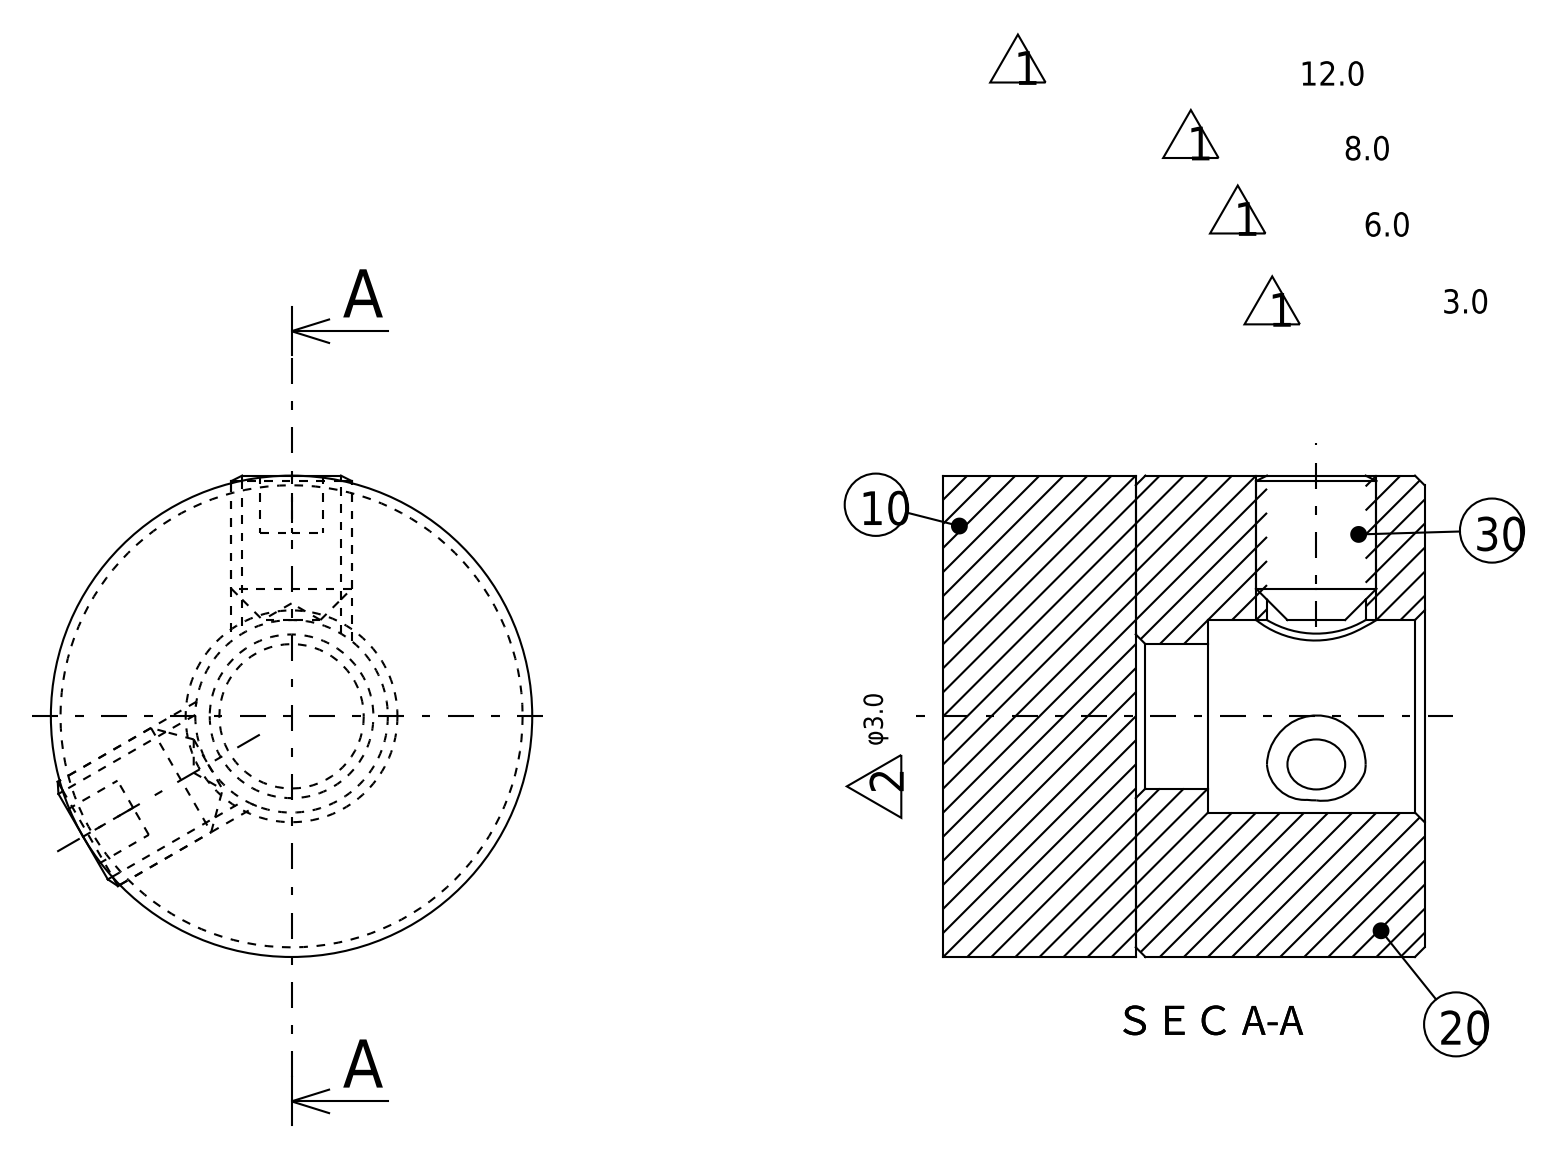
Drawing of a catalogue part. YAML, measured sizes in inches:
step_written_by: "PSStep 10.0 (CONFIG_CONTROL_DESIGN)"
units: inches
bodies: {solids: 5, faces: 51, planar: 29, cylindrical: 9, other: 13}
overall_size: [0.394, 0.394, 0.394]
volume: 0.045
surface_area: 1.25
round_holes:
  - {diameter: 0.081, count: 2}
  - {diameter: 0.118, count: 1}
  - {diameter: 0.157, count: 1}
round_bosses_or_shafts:
  - {diameter: 0.098, count: 2}
  - {diameter: 0.394, count: 1}
face_to_face_distances: [0.157, 0.236, 0.394, 0.051, 0.177, 0.059, 0.217, 0.047]
